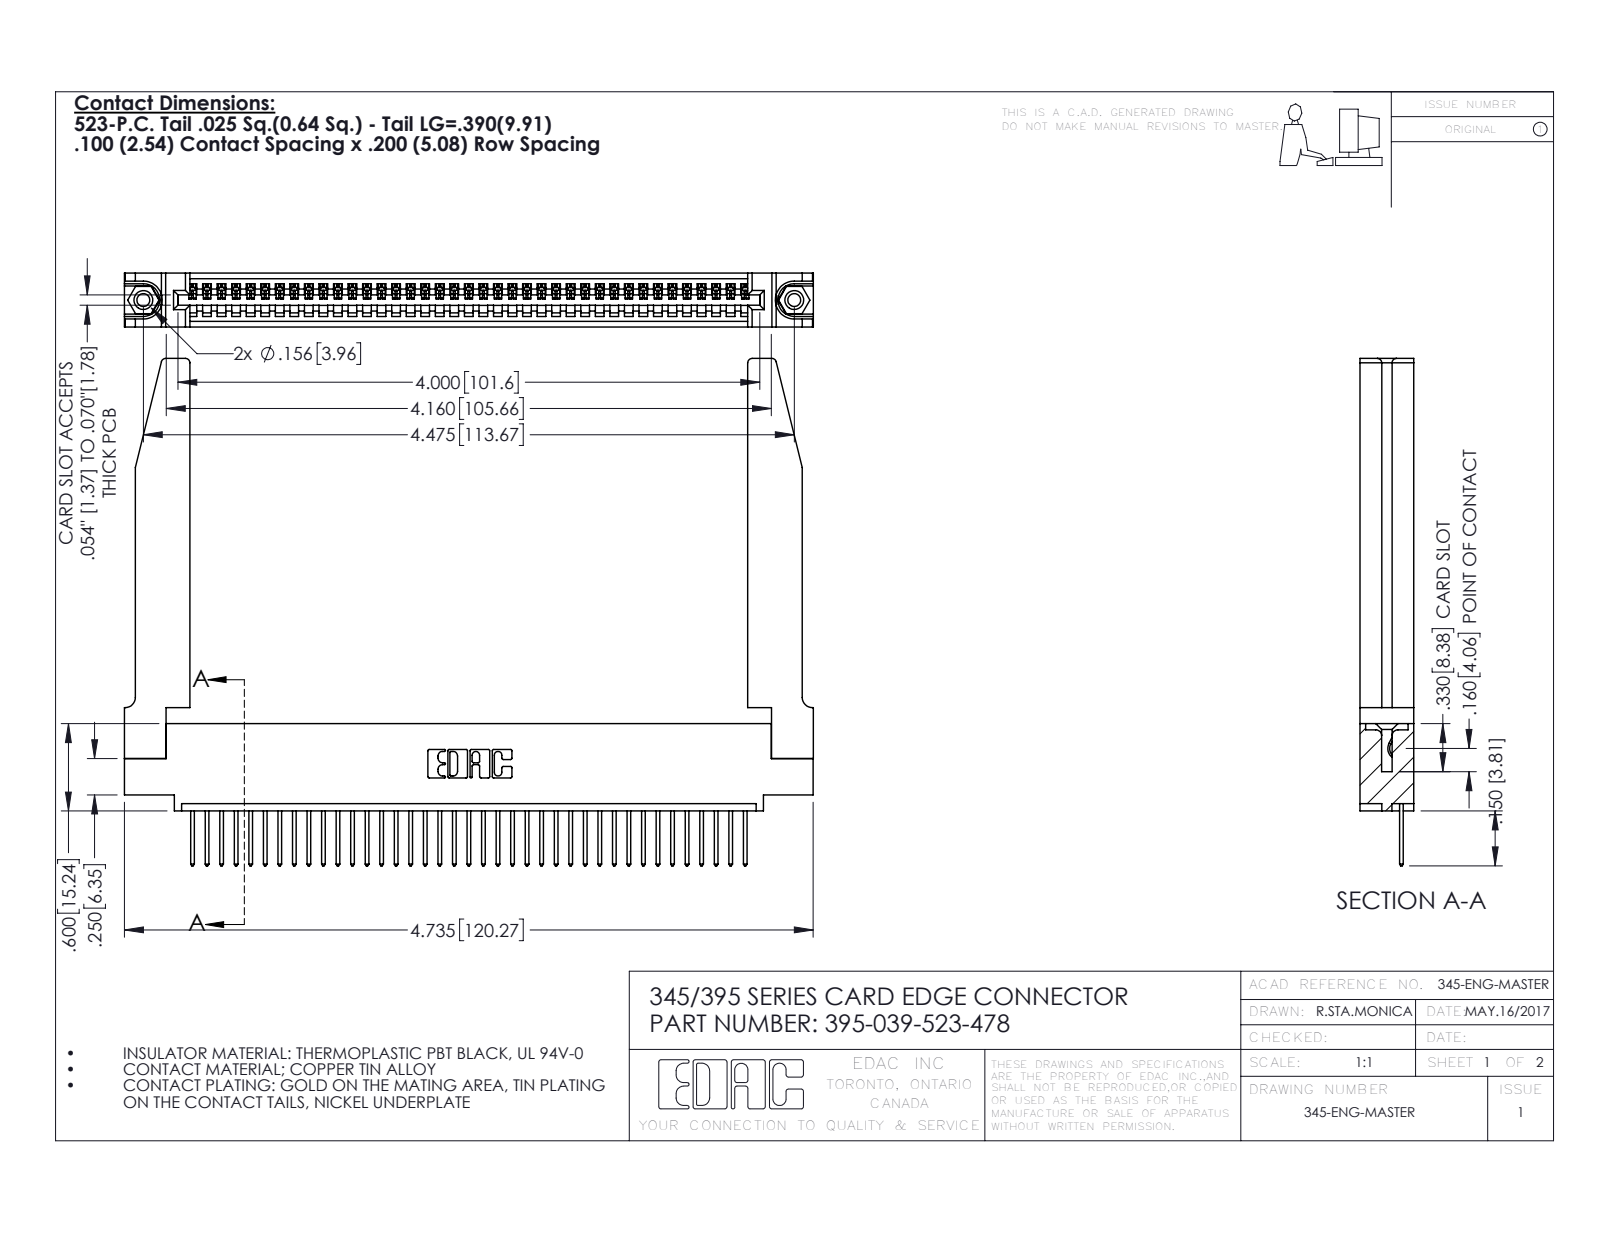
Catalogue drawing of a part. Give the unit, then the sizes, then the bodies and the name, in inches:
Units: inches
Overall size (bounding box): 4.736 × 3.487 × 0.37
Round holes (diameter × count): ⌀0.089 ×2, ⌀0.125 ×2, ⌀0.156 ×2, ⌀0.064 ×1
Round bosses / shafts (diameter × count): ⌀0.155 ×2
Partial cylindrical surfaces — rounded edges, fillets, slot ends (radius × count): R0.006 ×78, R0.01 ×78, R0.01 ×22, R0.03 ×8, R0.007 ×6, R0.031 ×6, R0.026 ×3, R0.031 ×2
Main face-to-face distances: 0.37, 0.072, 0.298, 0.098, 0.272, 0.025, 0.2, 0.225, 0.148, 0.15
Hole centre spacings: 0.27, 4.239, 4.475
Volume: 1.165 in³ · Surface area: 34.04 in²
Bodies: 44 solids, 2626 faces (1786 planar, 788 cylindrical, 52 other)
Part name (STEP PRODUCT): 345 Part_0.110 Offset - 0.156 Dia-TH; 345-250-001_345-250-001-102; 395-039-523-478; 345-220-078_345-220-078 (+1 more)
STEP written by: SolidWorks 2016 (CONFIG_CONTROL_DESIGN)
